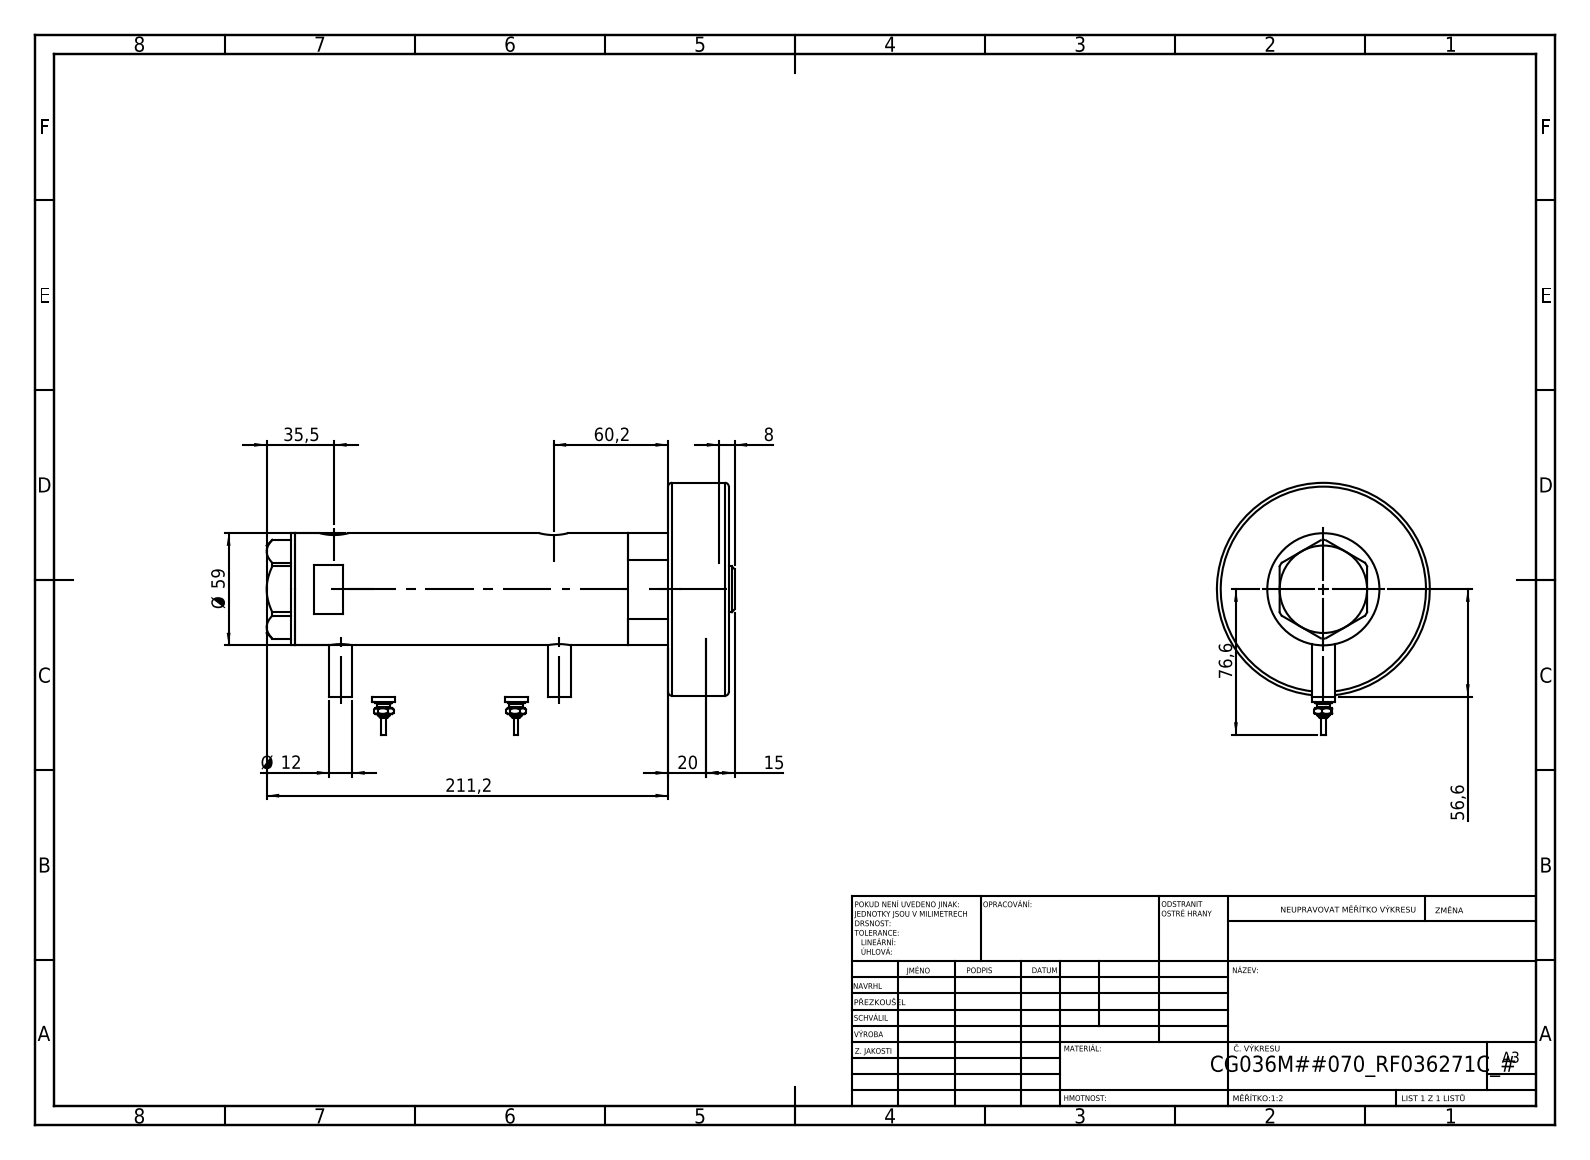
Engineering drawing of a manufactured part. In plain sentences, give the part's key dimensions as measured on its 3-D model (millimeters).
The part is named "V270CG_FRONT; V270CG_MIDDLE; Switch; V270CG_VC (+2 more)". Its 3-D file was written by "SolidWorks 2019 (CONFIG_CONTROL_DESIGN)". It is 7 solids with 222 faces: 81 planar, 73 cylindrical and 68 other. Overall it measures 246.2 by 132.6 by 112 millimeters. Its volume is 826 367 cubic millimeters and its surface area 148 029 square millimeters. Round holes: 2 of diameter 9.73, 2 of diameter 12.5, 2 of diameter 15, 1 of diameter 8.5, 1 of diameter 25, 1 of diameter 26.5, 1 of diameter 36, 1 of diameter 40, 1 of diameter 48, 1 of diameter 52. Round bosses or shafts: 4 of diameter 12, 2 of diameter 9, 2 of diameter 7, 2 of diameter 4.5, 2 of diameter 2.5, 1 of diameter 112, 1 of diameter 59, 1 of diameter 46. The main face-to-face distances are 32, 196.2, 228.2, 137.2, 59, 91, 23.5, 113.7, 172.7, 204.7. The hole center spacings are 2.9, 3.5, 112, 114.9, 115.5, 118.4.
